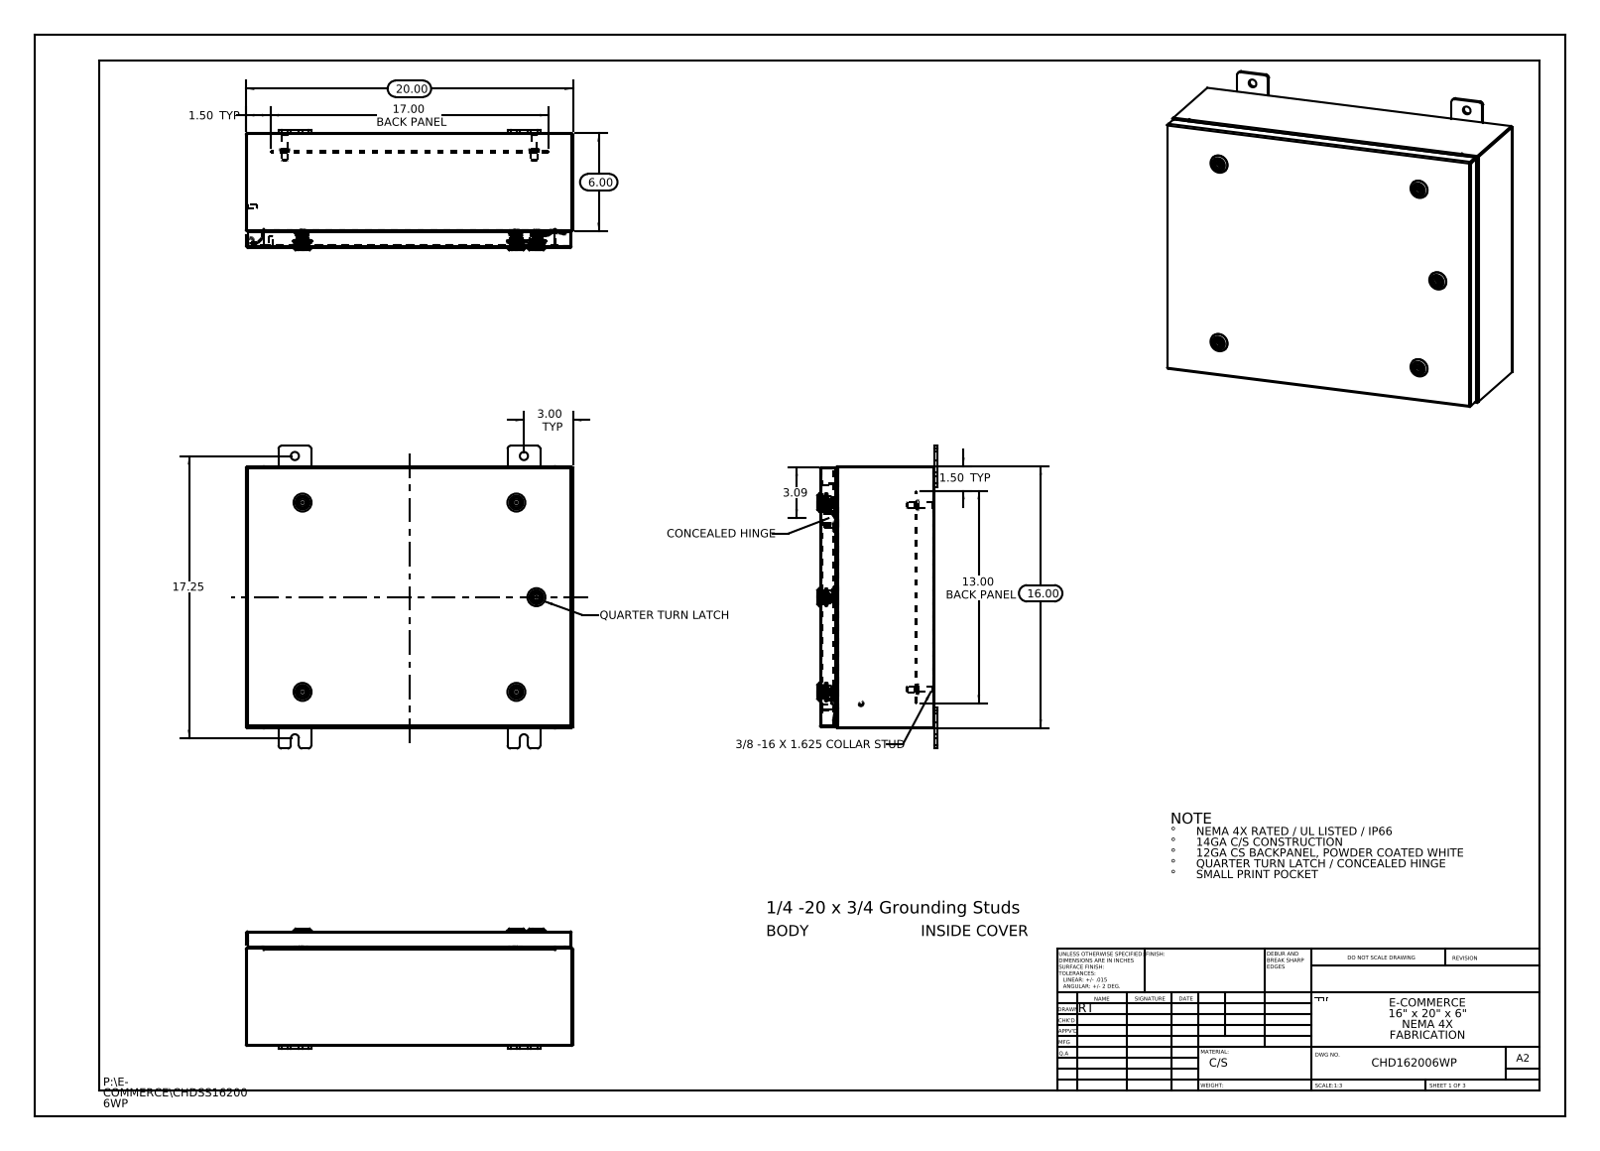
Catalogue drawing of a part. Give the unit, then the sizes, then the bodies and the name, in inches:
Units: inches
Overall size (bounding box): 20 × 18.5 × 7.356
Round holes (diameter × count): ⌀0.5 ×8, ⌀0.197 ×5, ⌀0.394 ×5, ⌀0.4 ×5, ⌀0.63 ×5, ⌀0.787 ×5, ⌀0.136 ×2
Round bosses / shafts (diameter × count): ⌀0.236 ×7, ⌀1.102 ×5, ⌀0.78 ×5, ⌀0.626 ×5, ⌀0.61 ×5, ⌀0.531 ×5, ⌀0.392 ×5, ⌀0.114 ×5
Partial cylindrical surfaces — rounded edges, fillets, slot ends (radius × count): R0.006 ×165, R0.118 ×165, R0.028 ×60, R0.19 ×24, R0.02 ×20, R0.197 ×20, R0.013 ×18, R0.088 ×18
Main face-to-face distances: 0.075, 0.074, 7.01, 6.935, 6.936, 6.861, 15.925, 1, 1.075, 5.861
Hole centre spacings: 1.858, 3.065, 5.627, 11.25, 11.569, 13.015, 13.069, 13.164
Volume: 123.9 in³ · Surface area: 3 102 in²
Bodies: 46 solids, 4516 faces (1318 planar, 1408 cylindrical, 1790 other)
Part name (STEP PRODUCT): CHDSS162006WP Body; CHDSS162006WP Top; CHDSS162006WP Cover; Washer-221320-IB-Industrilas_Washer-221320-IB-Industrilas (+8 more)
STEP written by: SolidWorks 2013 (CONFIG_CONTROL_DESIGN)
